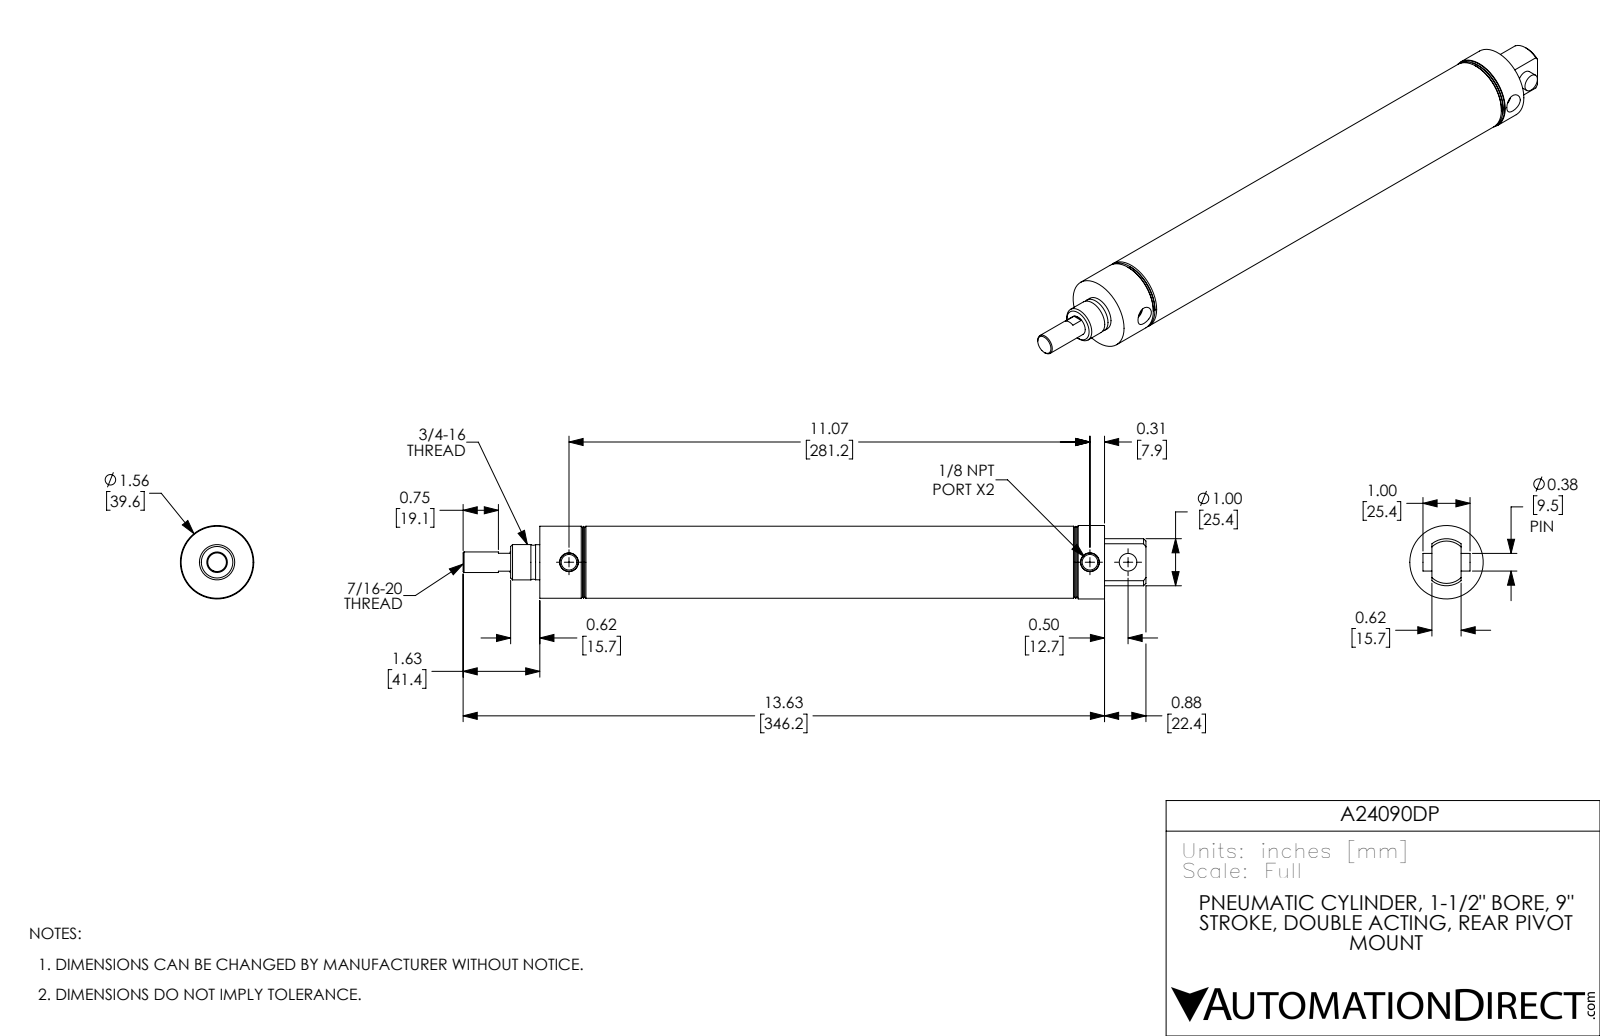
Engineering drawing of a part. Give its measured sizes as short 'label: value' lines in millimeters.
name: A24090DP; A24090DP-Pin; A24090DP-Rod; A24090DP-MainBody
written by: SolidWorks 2017 (AUTOMOTIVE_DESIGN)
unit: mm
bodies: 3 solids, 84 faces (22 planar, 28 cylindrical, 34 other)
size: 368.6 × 39.6 × 39.6
volume: 137 700 mm³; area: 91 290 mm²
holes: 2× ⌀8.4, 1× ⌀9.5, 1× ⌀11.1, 1× ⌀38.1
bosses: 1× ⌀39.6, 1× ⌀38.9, 1× ⌀19.1, 1× ⌀18.9
rounds: 1× R12.7
face distances: 31.8, 273.1, 241.3, 12.7, 228.6, 260.4, 44.5, 304.8, 15.7, 22.4
hole spacings: 20.6, 281.2, 301.8
